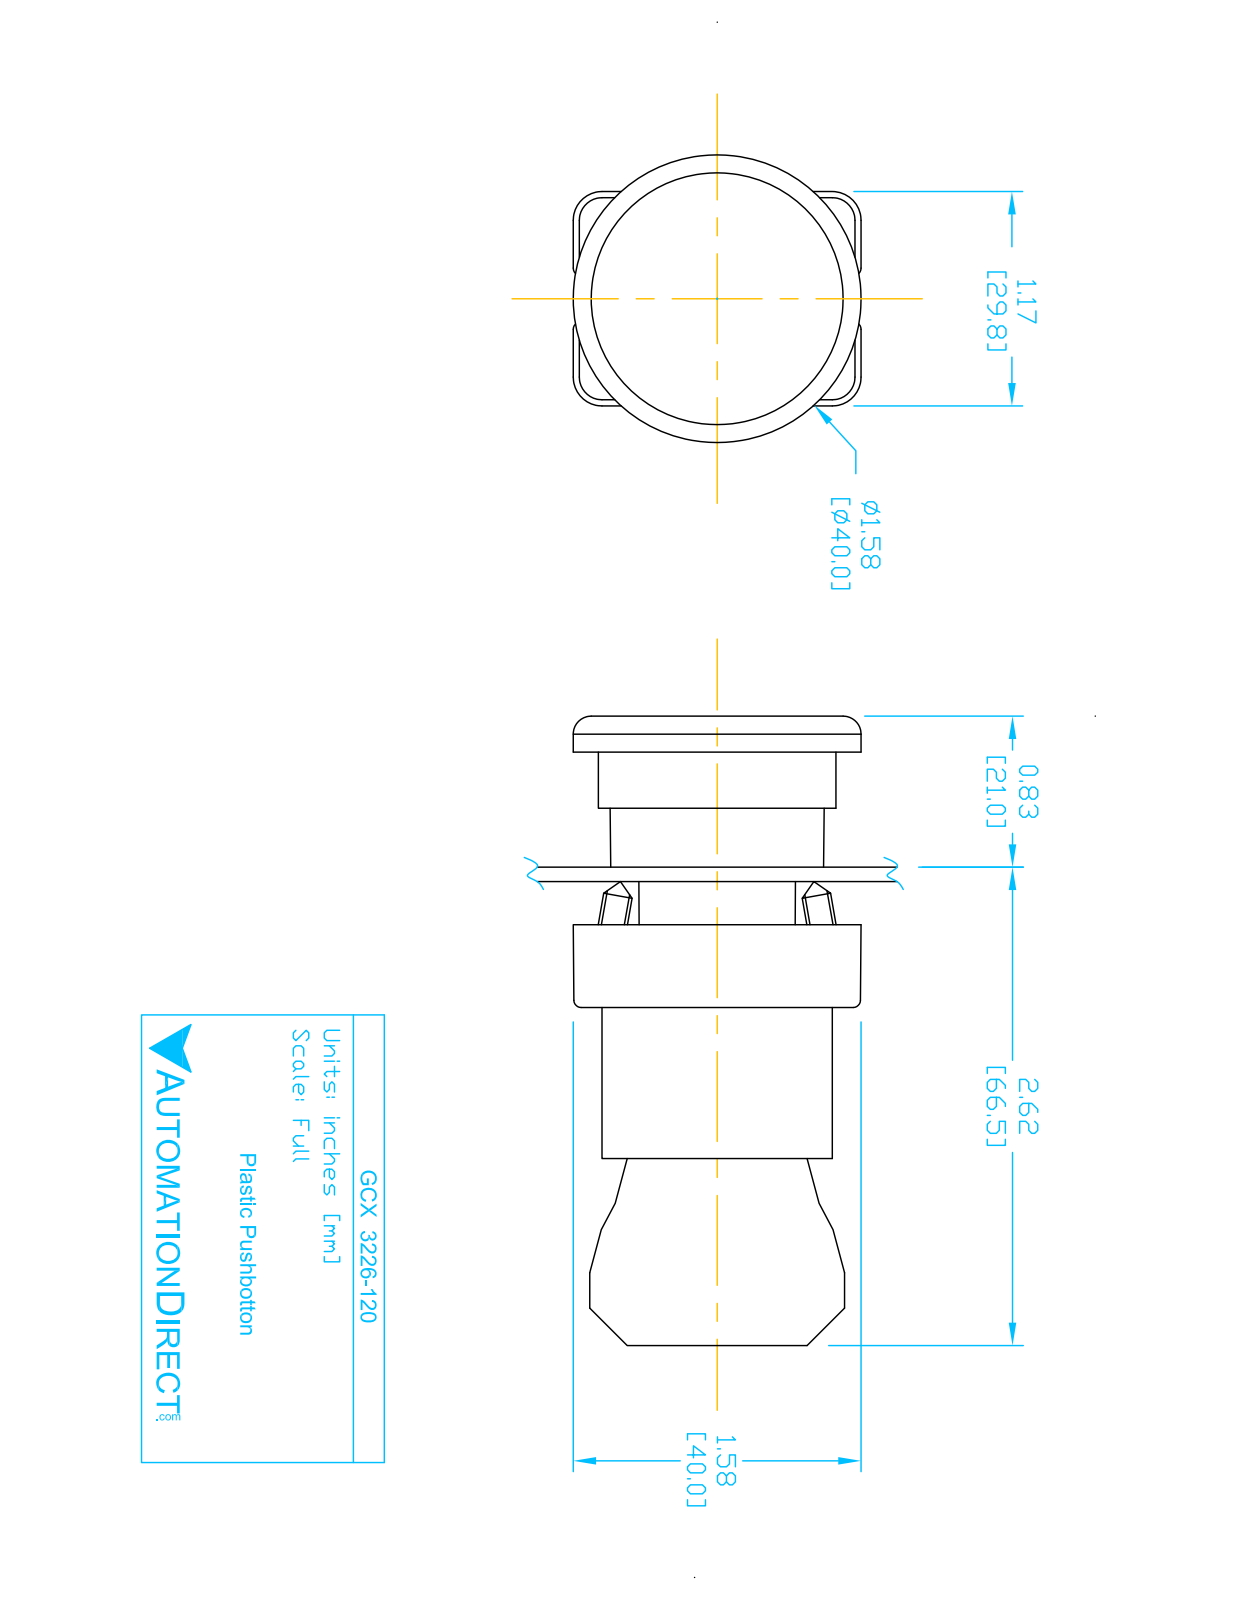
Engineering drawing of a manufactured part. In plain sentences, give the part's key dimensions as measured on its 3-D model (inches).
The part is named "GCX3226-120; ECX1050; ecx1030; ECX3029-2 (+1 more)". Its 3-D file was written by "SolidWorks 2016 (AUTOMOTIVE_DESIGN)". It is 7 solids with 431 faces: 252 planar, 146 cylindrical and 33 other. Overall it measures 3.469 by 1.581 by 1.575 inches. Its volume is 2.895 cubic inches and its surface area 40.89 square inches. Round holes: 2 of diameter 0.079, 2 of diameter 0.124, 2 of diameter 0.13, 1 of diameter 0.087, 1 of diameter 0.197, 1 of diameter 0.469, 1 of diameter 0.878, 1 of diameter 0.888, 1 of diameter 1.024, 1 of diameter 1.181. Round bosses or shafts: 4 of diameter 0.157, 1 of diameter 1.299, 1 of diameter 1.175, 1 of diameter 0.945, 1 of diameter 0.856, 1 of diameter 0.78, 1 of diameter 0.504. Partial cylindrical surfaces (rounded edges, fillets, slot ends): 24 of radius 0.059, 12 of radius 0.041, 12 of radius 0.124, 12 of radius 0.157, 8 of radius 0.039, 2 of radius 0.128, 1 of radius 0.02, 1 of radius 0.063. The main face-to-face distances are 0.827, 2.445, 1.618, 0.579, 2.287, 1.461, 0.157, 0.587, 0.031, 1.165. The hole center spacings are 0.236, 0.539, 0.472, 0.484.
